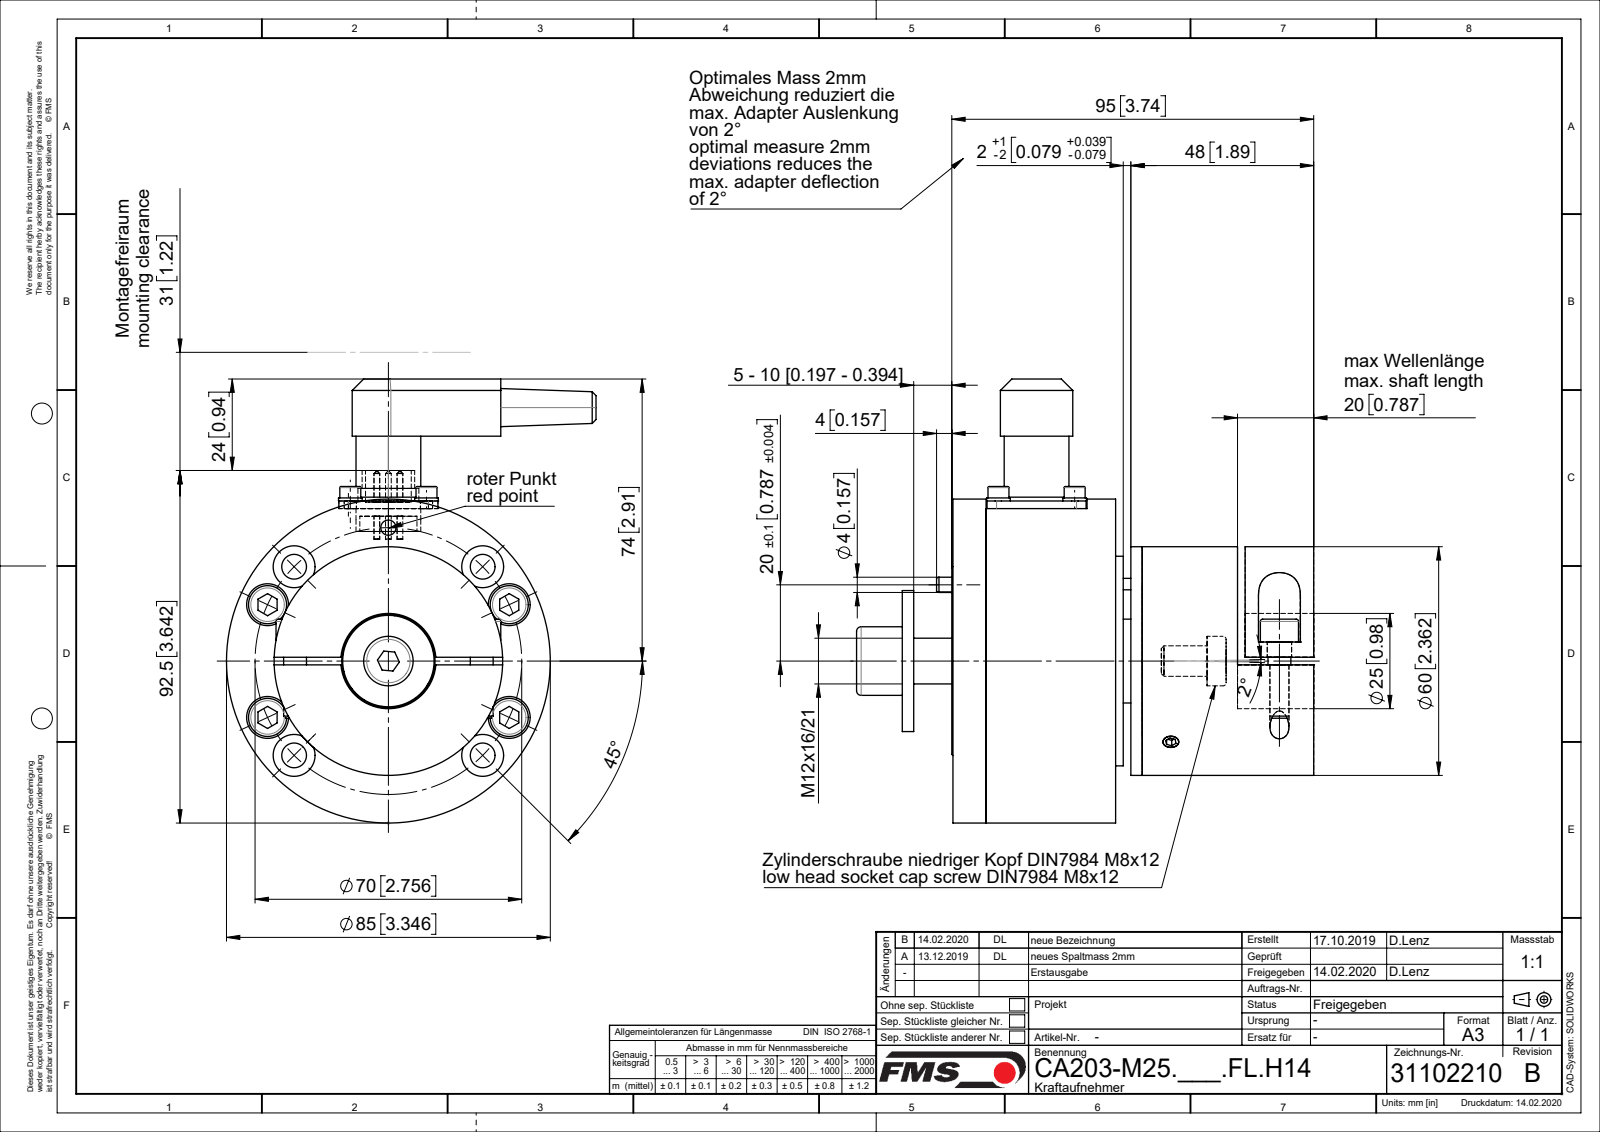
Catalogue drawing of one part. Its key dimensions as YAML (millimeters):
part_name: "C0705311_DM25; C0709081; C0612056; C0709072 (+8 more)"
step_written_by: "Mechanical Desktop 2009 (CONFIG_CONTROL_DESIGN)"
units: millimeters
bodies: {solids: 37, faces: 685, planar: 229, cylindrical: 315, other: 141}
overall_size: [120.5, 116.5, 97]
volume: 323828
surface_area: 112583
round_holes:
  - {diameter: 2.6, count: 8}
  - {diameter: 6.5, count: 8}
  - {diameter: 11, count: 8}
  - {diameter: 5.15, count: 6}
  - {diameter: 2, count: 5}
  - {diameter: 3.2, count: 4}
  - {diameter: 3.6, count: 4}
  - {diameter: 4, count: 4}
  - {diameter: 7, count: 4}
  - {diameter: 6.4, count: 2}
  - {diameter: 3, count: 1}
  - {diameter: 4.33, count: 1}
round_bosses_or_shafts:
  - {diameter: 6, count: 10}
  - {diameter: 3, count: 8}
  - {diameter: 10, count: 6}
  - {diameter: 1.5, count: 5}
  - {diameter: 6.2, count: 4}
  - {diameter: 5.5, count: 4}
  - {diameter: 5, count: 4}
  - {diameter: 85, count: 1}
partial_cylinders:
  - {radius: 2.5, count: 4}
  - {radius: 5, count: 2}
  - {radius: 5.5, count: 2}
  - {radius: 9.5, count: 1}
face_to_face_distances: [45, 49.5, 9, 2, 11.5, 31.5, 10, 43, 1.5, 40.5]
hole_center_spacings: [20, 24.78, 25.2, 32.8, 35, 51.14, 56.46, 6]
